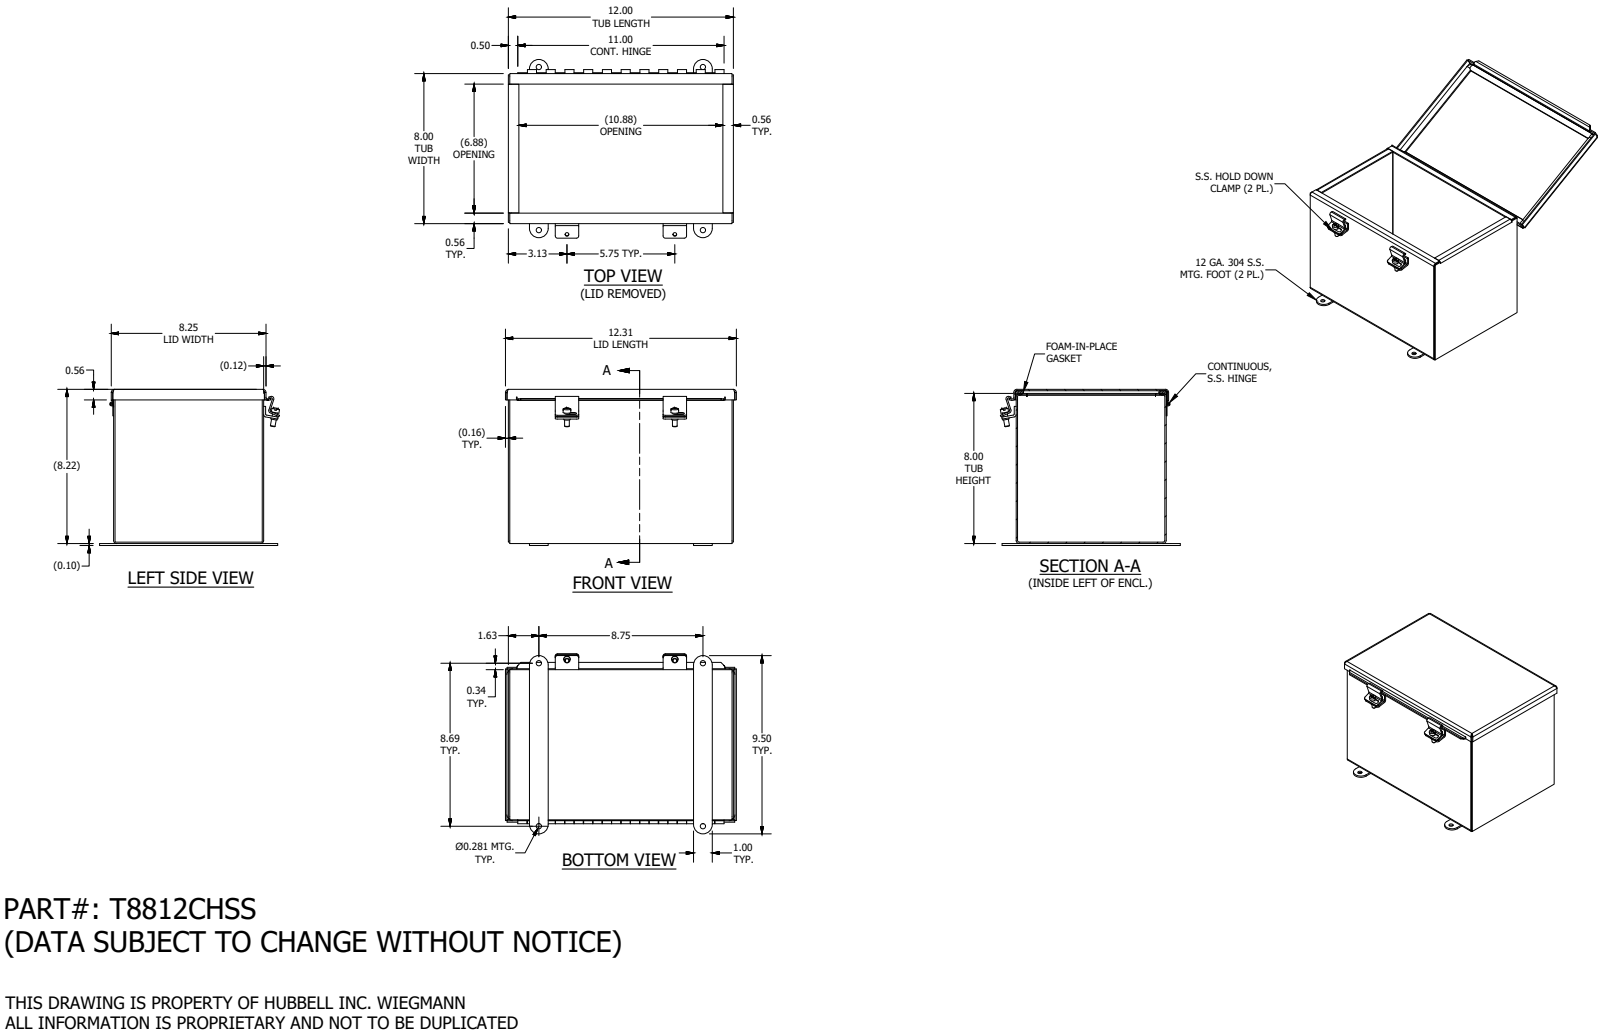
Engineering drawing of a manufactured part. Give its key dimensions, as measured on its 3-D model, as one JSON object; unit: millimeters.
{"part_name": "T8812CHSS", "step_written_by": "SolidWorks 2019 (AUTOMOTIVE_DESIGN)", "units": "millimeters", "bodies": {"solids": 16, "faces": 406, "planar": 245, "cylindrical": 129, "other": 32}, "overall_size": [312.8, 243.8, 211.4], "volume_mm3": 770000, "surface_area_mm2": 803200, "round_holes": [[2.8, 4], [7.1, 4], [5, 2], [2.9, 1]], "round_bosses_or_shafts": [[10.4, 2], [8.7, 2], [6.4, 2], [5.1, 1], [2.5, 1]], "partial_cylinders_radius": [[2.4, 11], [4.3, 11], [2.2, 8], [3.2, 8], [3.4, 4], [6.1, 4], [12.7, 4], [1.6, 3]], "face_to_face_distances": [1.9, 201.3, 206.9, 302.9, 199.4, 203.2, 208.7, 205, 301, 304.8], "hole_center_spacings": [146.1, 19.1, 220.6, 222.3, 313.2, 127, 165.1]}
